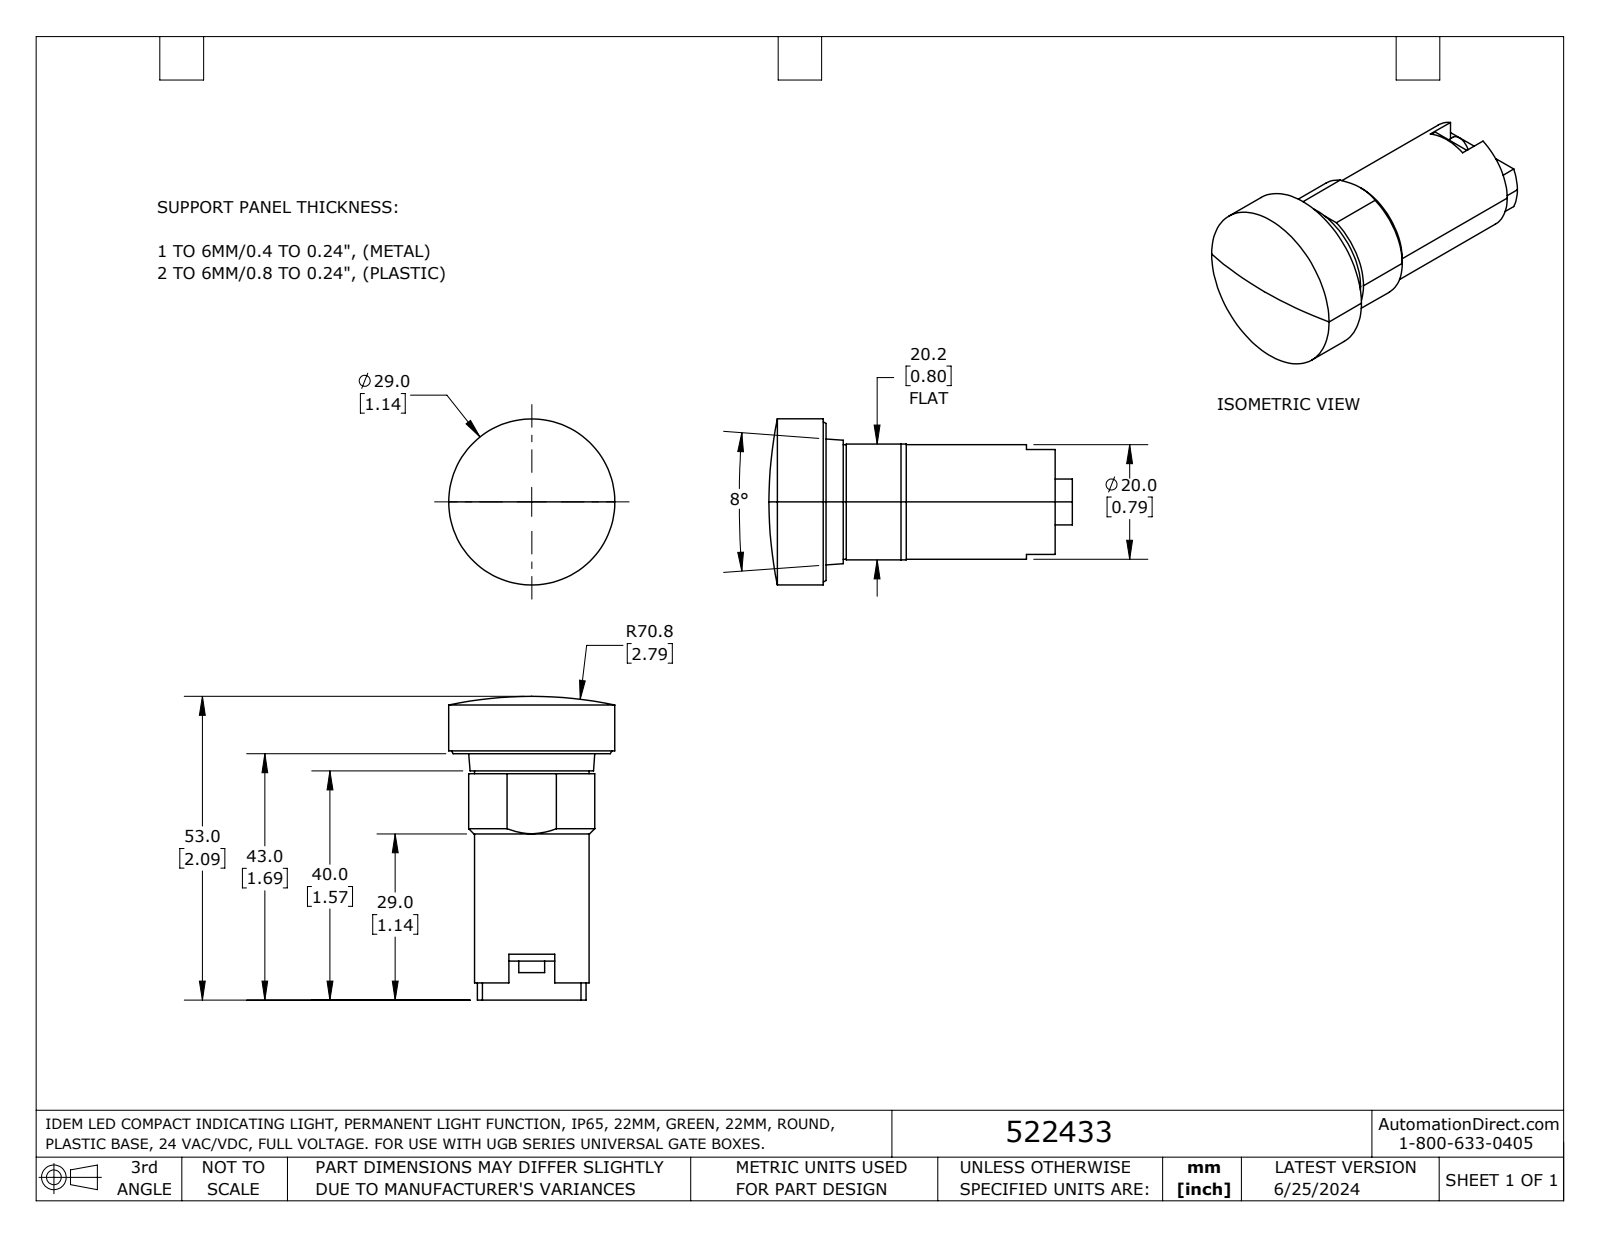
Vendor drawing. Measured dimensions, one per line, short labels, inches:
name: 522433
written by: SolidWorks 2023 (AUTOMOTIVE_DESIGN)
unit: in
bodies: 1 solid, 50 faces (24 planar, 18 cylindrical, 8 other)
size: 2.087 × 1.142 × 1.142
volume: 1.192 in³; area: 7.789 in²
bosses: 2× ⌀0.177, 1× ⌀1.142, 1× ⌀0.787
rounds: 1× R0.374, 1× R0.433
face distances: 0.241, 0.556, 1.693, 0.315, 0.118, 1.575, 0.138, 0.02, 0.797, 1.437
